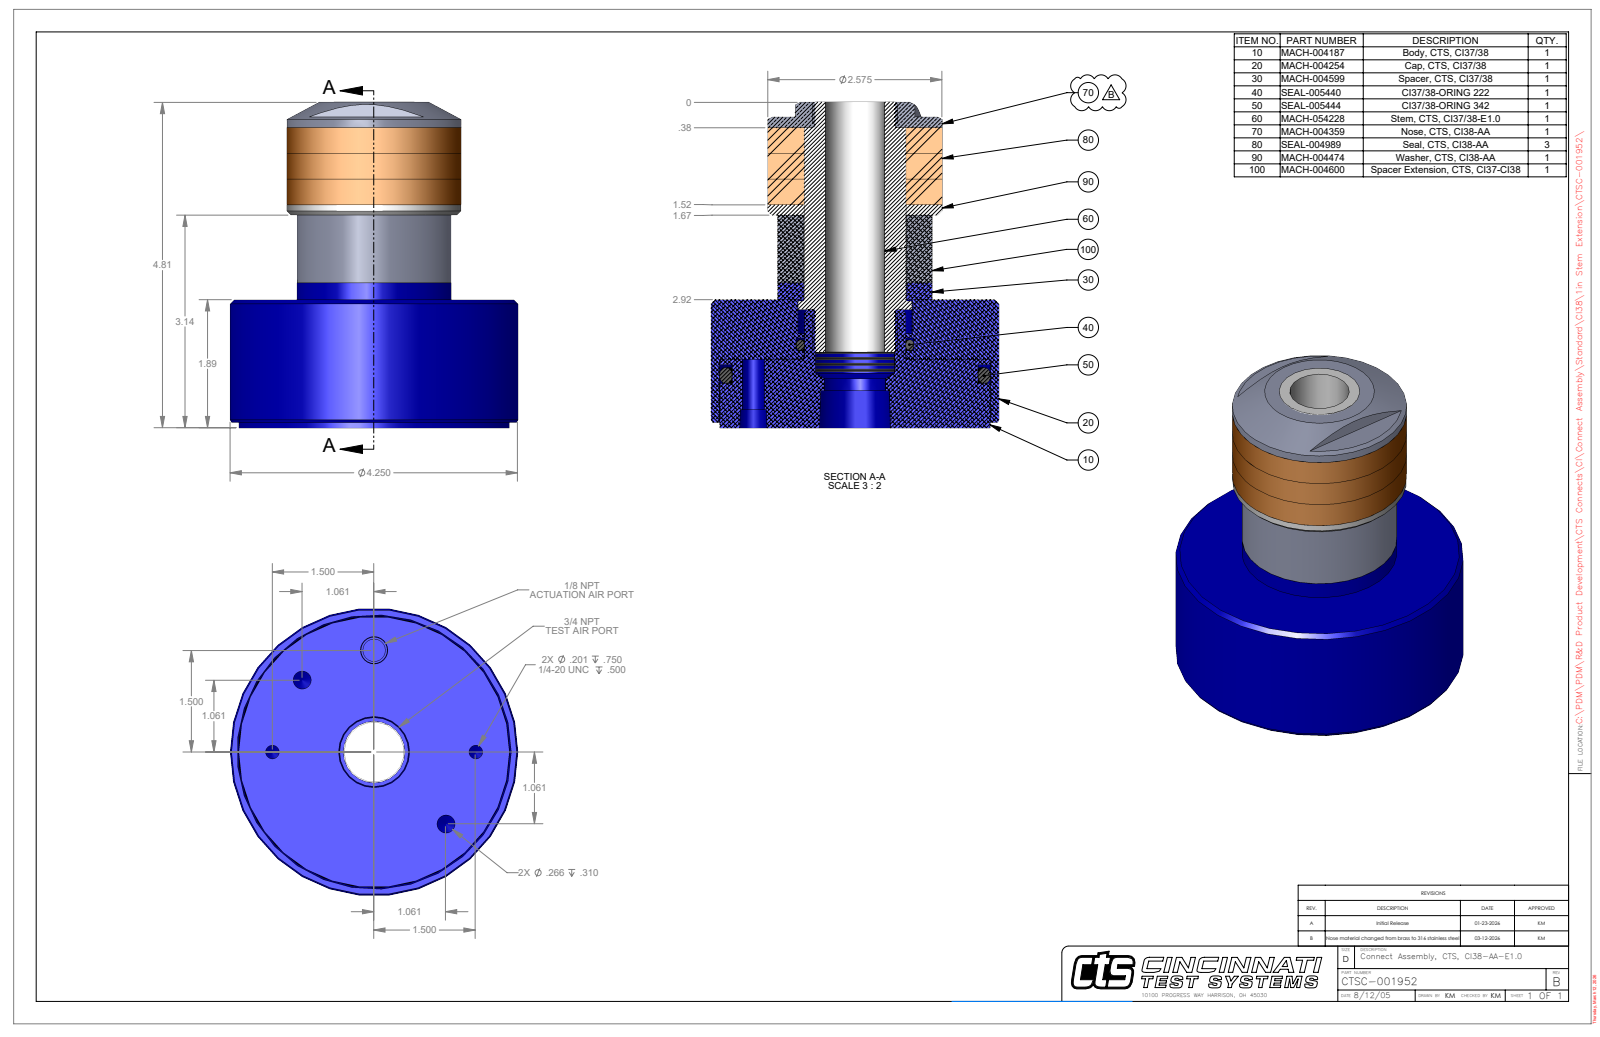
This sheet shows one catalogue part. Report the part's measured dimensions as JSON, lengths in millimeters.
{"part_name": "CTSC-001952", "step_written_by": "SolidWorks 2023 (AUTOMOTIVE_DESIGN)", "units": "millimeters", "bodies": {"solids": 8, "faces": 77, "planar": 37, "cylindrical": 28, "other": 12}, "overall_size": [122.25, 107.95, 107.95], "volume_mm3": 600672, "surface_area_mm2": 104386, "round_holes": [[5.11, 2], [6.75, 2], [22.35, 1], [23.01, 1], [29.77, 1], [37.97, 1], [37.97, 1], [38.35, 1], [42.88, 1], [101.6, 1]], "round_bosses_or_shafts": [[107.95, 1], [101.4, 1], [65.41, 1], [57.94, 1], [42.52, 1], [38.05, 1], [31.75, 1]], "face_to_face_distances": [9.65, 19.31, 48.08, 112.65, 64.57, 103, 54.92, 93.34, 45.26, 9.66], "hole_center_spacings": [38.1, 29.16, 70.4, 76.2]}
